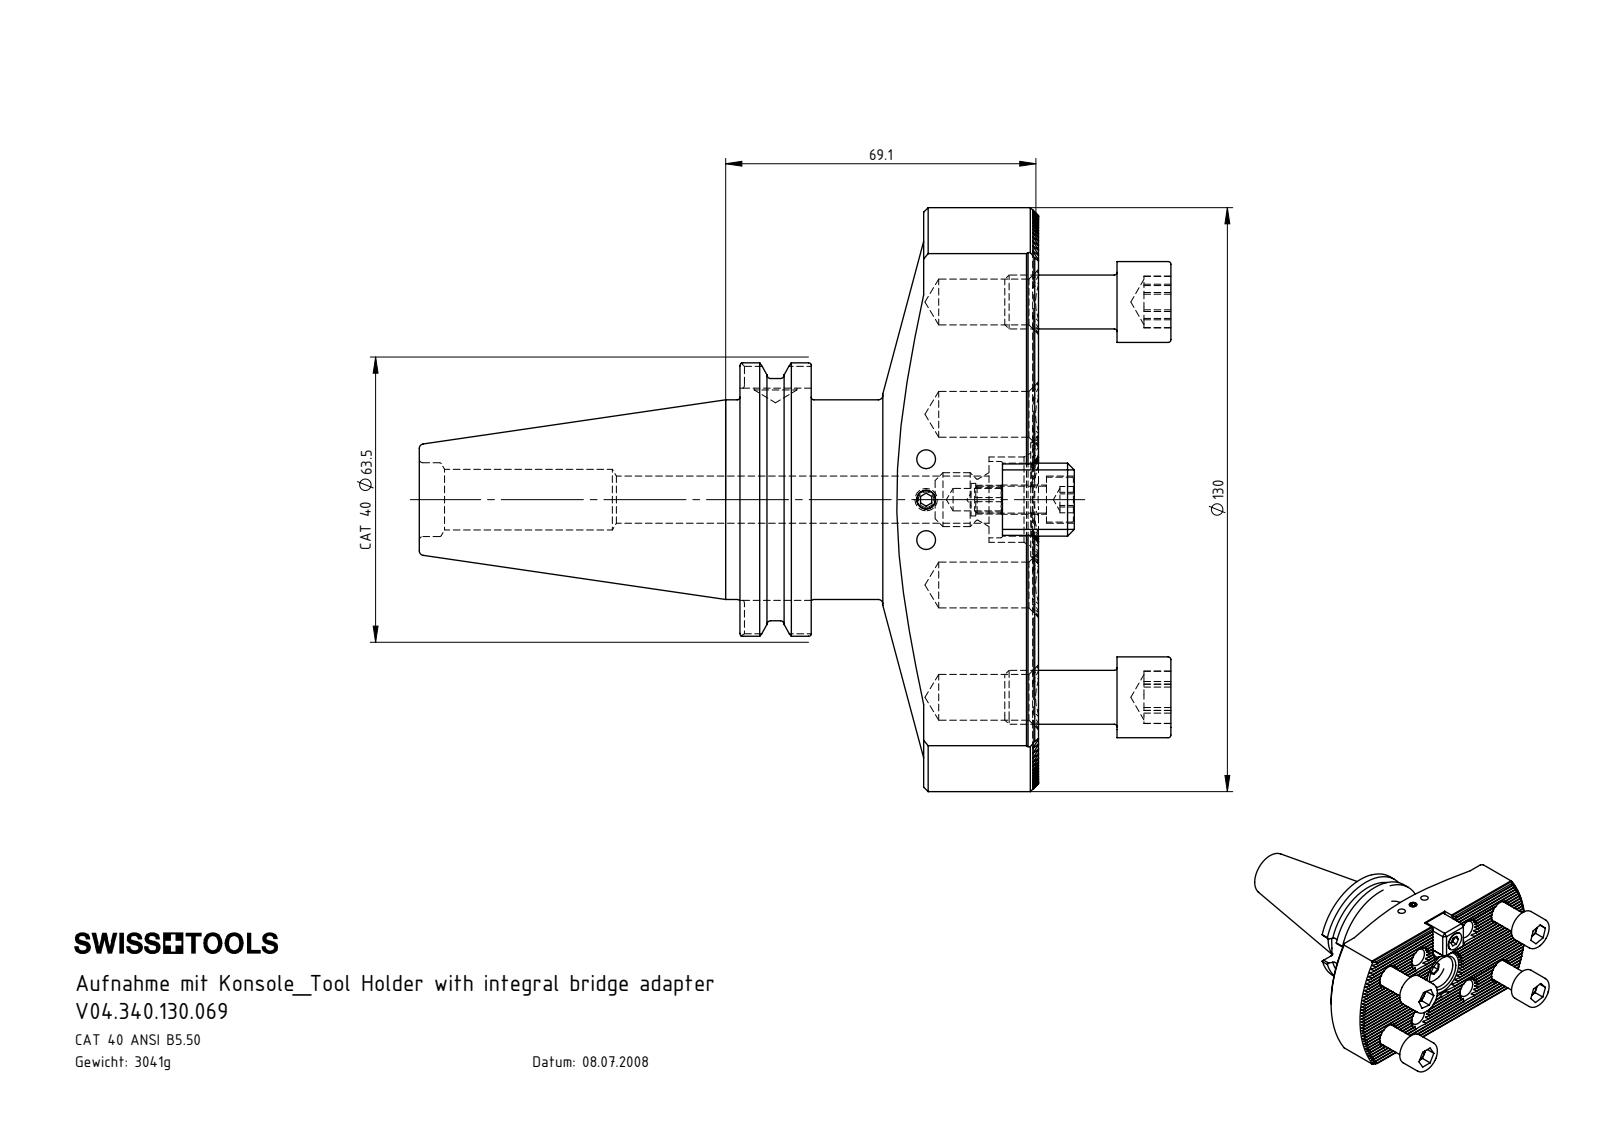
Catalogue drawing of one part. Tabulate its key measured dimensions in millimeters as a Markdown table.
| quantity | value |
| --- | --- |
| part name | CT4.Ko1.K01.069; Ko1-ER1.001.016_A; ISO 4762 M6 x 16; ISO 4762 M12 x 25 (+3 more) |
| STEP written by | SolidWorks 2017 (AUTOMOTIVE_DESIGN) |
| units | millimeters |
| bodies | 10 solids, 746 faces (496 planar, 161 cylindrical, 89 other) |
| overall size | 167.42 × 130 × 70 |
| volume | 387 391 mm³ |
| surface area | 72 839 mm² |
| round holes (diameter × count) | 10.2 × 8, 4.2 × 3, 10.5 × 2, 5 × 1, 6.5 × 1, 7.24 × 1, 9.5 × 1, 13.5 × 1, 16.43 × 1, 19 × 1 |
| round bosses / shafts (diameter × count) | 12 × 5, 18 × 4, 63.5 × 1, 56.36 × 1, 44.45 × 1, 17 × 1, 10 × 1, 6 × 1 |
| partial cylindrical surfaces (radius × count) | 0.14 × 34, 0.8 × 8, 7.95 × 1, 65 × 1 |
| main face-to-face distances | 1.73, 17.32, 70, 8.66, 3.46, 5.2, 6.93, 15.59, 19.05, 3.47 |
| hole center spacings | 25, 27.59, 40, 47.17, 48.33, 63, 74.63, 9 |
